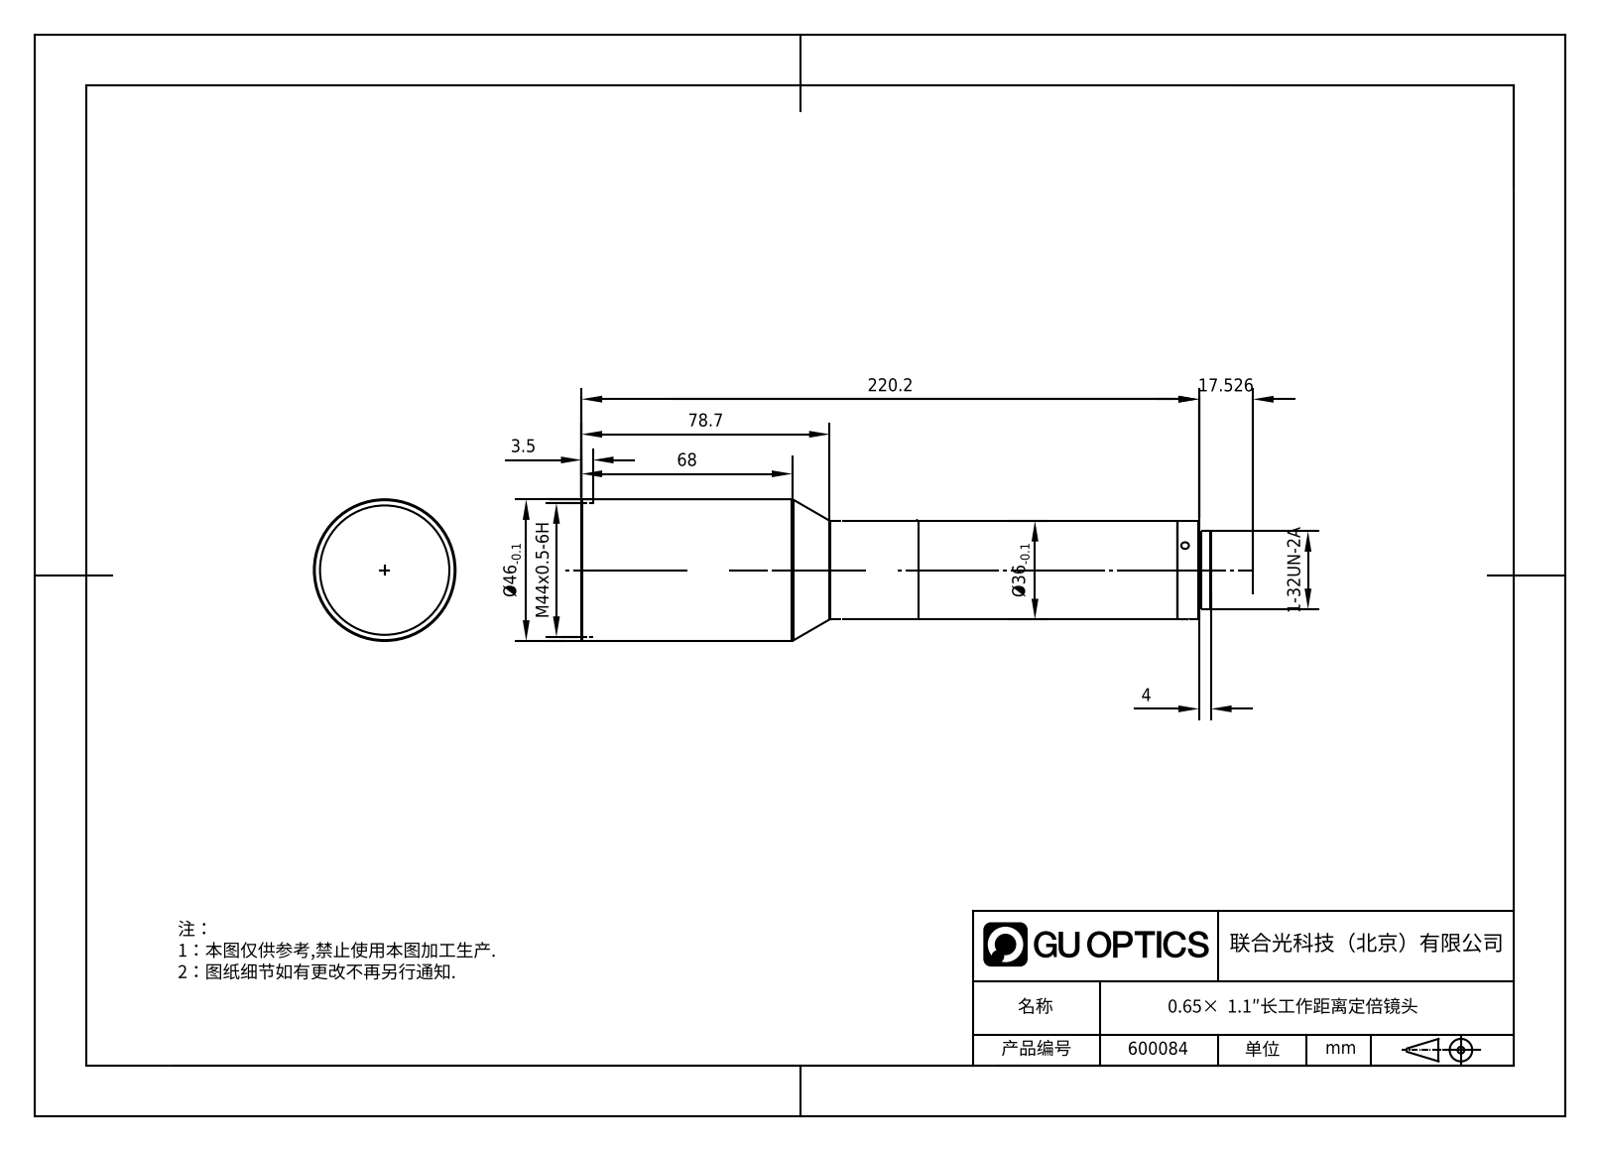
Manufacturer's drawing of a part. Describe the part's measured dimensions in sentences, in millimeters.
The part is named "600084". Its 3-D file was written by "SolidWorks 2020 (CONFIG_CONTROL_DESIGN)". It is 2 solids with 28 faces: 7 planar, 12 cylindrical and 9 other. Overall it measures 224.15 by 46 by 46 millimeters. Its volume is 266 180 cubic millimeters and its surface area 34 634 square millimeters. Round holes: 3 of diameter 2.5, 1 of diameter 42. Round bosses or shafts: 1 of diameter 46, 1 of diameter 36, 1 of diameter 25.4, 1 of diameter 24.6. Partial cylindrical surfaces (rounded edges, fillets, slot ends): 1 of radius 16.75. The main face-to-face distances are 211.15, 215.15, 4, 9, 220.15, 224.15, 220.95, 211.95, 0.8, 3.2.
